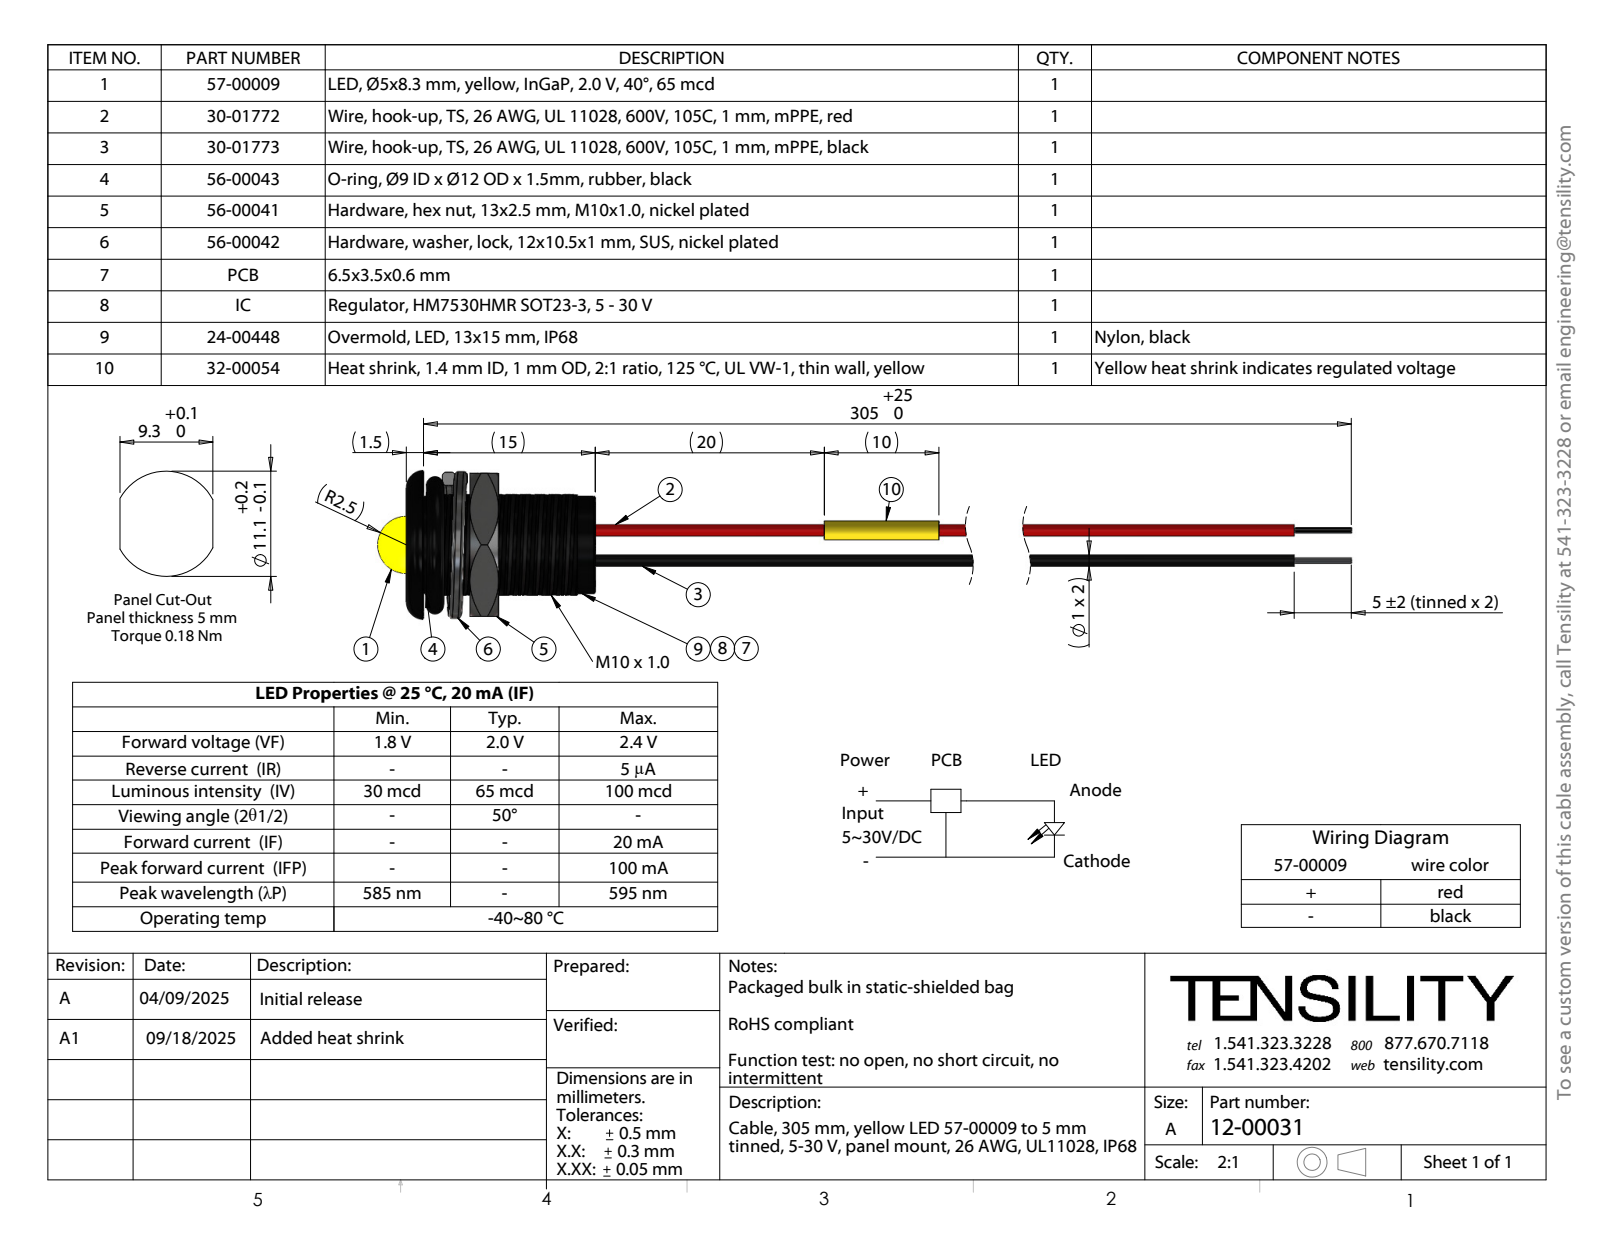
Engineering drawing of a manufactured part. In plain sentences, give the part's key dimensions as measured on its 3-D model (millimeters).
The part is named "56-00041; 56-00042_Split washer; 30-01773_stripped and tinned; 24-00448 (+4 more)". Its 3-D file was written by "SolidWorks 2021 (CONFIG_CONTROL_DESIGN)". It is 57 solids with 514 faces: 185 planar, 246 cylindrical and 83 other. Overall it measures 173.99 by 14.43 by 12.99 millimeters. Its volume is 1 769 cubic millimeters and its surface area 6 568 square millimeters. Round holes: 2 of diameter 1. Round bosses or shafts: 2 of diameter 1, 2 of diameter 0.83, 1 of diameter 8.5, 1 of diameter 5. Partial cylindrical surfaces (rounded edges, fillets, slot ends): 1 of radius 4.33, 1 of radius 5. The main face-to-face distances are 1.5, 16.5, 15, 12.5, 8.06, 6.56, 8.44, 5.56, 4.06, 2.5. The hole center spacings are 0.36, 0.38, 0.33, 2.43, 2.35, 2.48, 2.52, 2.56.
